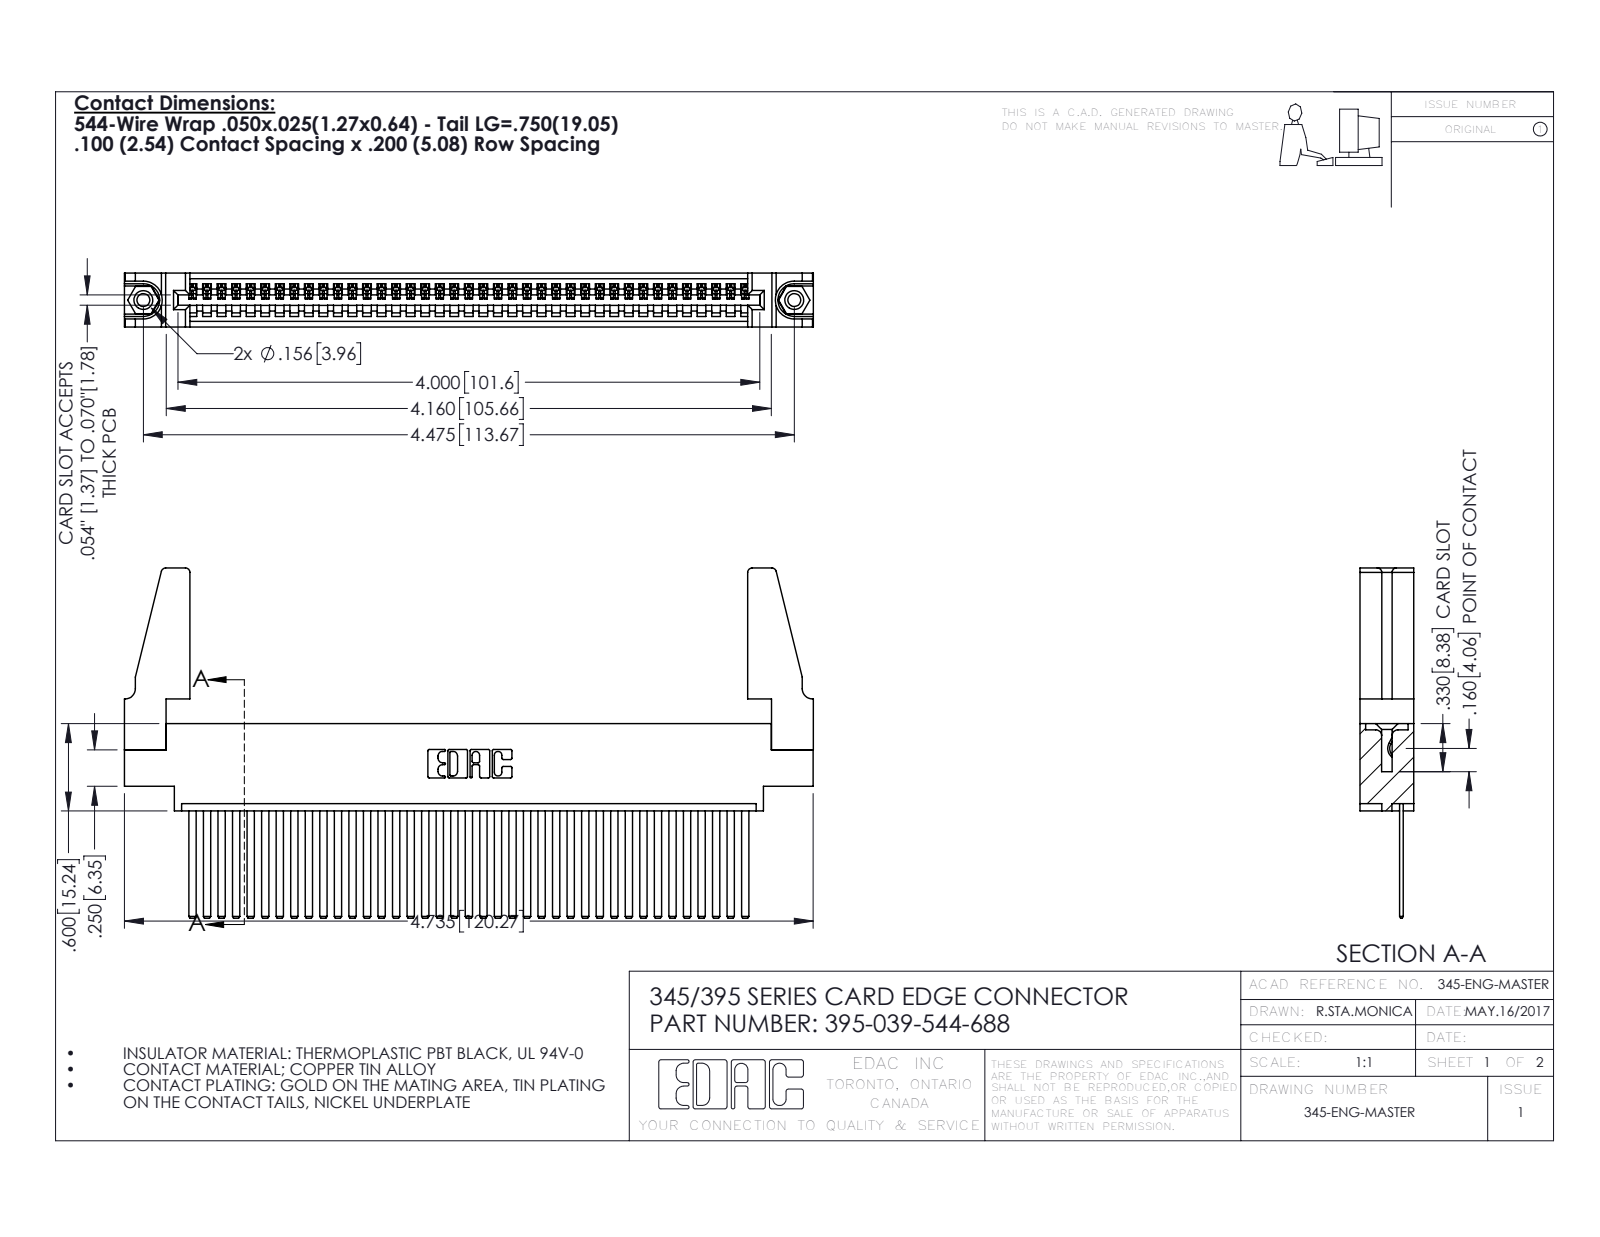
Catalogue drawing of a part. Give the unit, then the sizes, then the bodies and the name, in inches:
Units: inches
Overall size (bounding box): 4.736 × 2.407 × 0.37
Round holes (diameter × count): ⌀0.089 ×2, ⌀0.125 ×2, ⌀0.156 ×2, ⌀0.064 ×1
Round bosses / shafts (diameter × count): ⌀0.155 ×2
Partial cylindrical surfaces — rounded edges, fillets, slot ends (radius × count): R0.006 ×78, R0.01 ×22, R0.03 ×8, R0.007 ×6, R0.031 ×6, R0.026 ×3, R0.031 ×2, R0.04 ×2
Main face-to-face distances: 0.072, 0.298, 0.37, 0.098, 0.272, 0.025, 0.2, 0.225, 0.175, 0.149
Hole centre spacings: 0.27, 4.239, 4.475
Volume: 0.915 in³ · Surface area: 31.27 in²
Bodies: 44 solids, 2282 faces (1560 planar, 706 cylindrical, 16 other)
Part name (STEP PRODUCT): 345 Part_0.170 Offset - 0.156 Dia-TH; 345-250-001_345-250-001-102; 395-039-544-688; 345-220-078_345-220-088 (+1 more)
STEP written by: SolidWorks 2016 (CONFIG_CONTROL_DESIGN)
